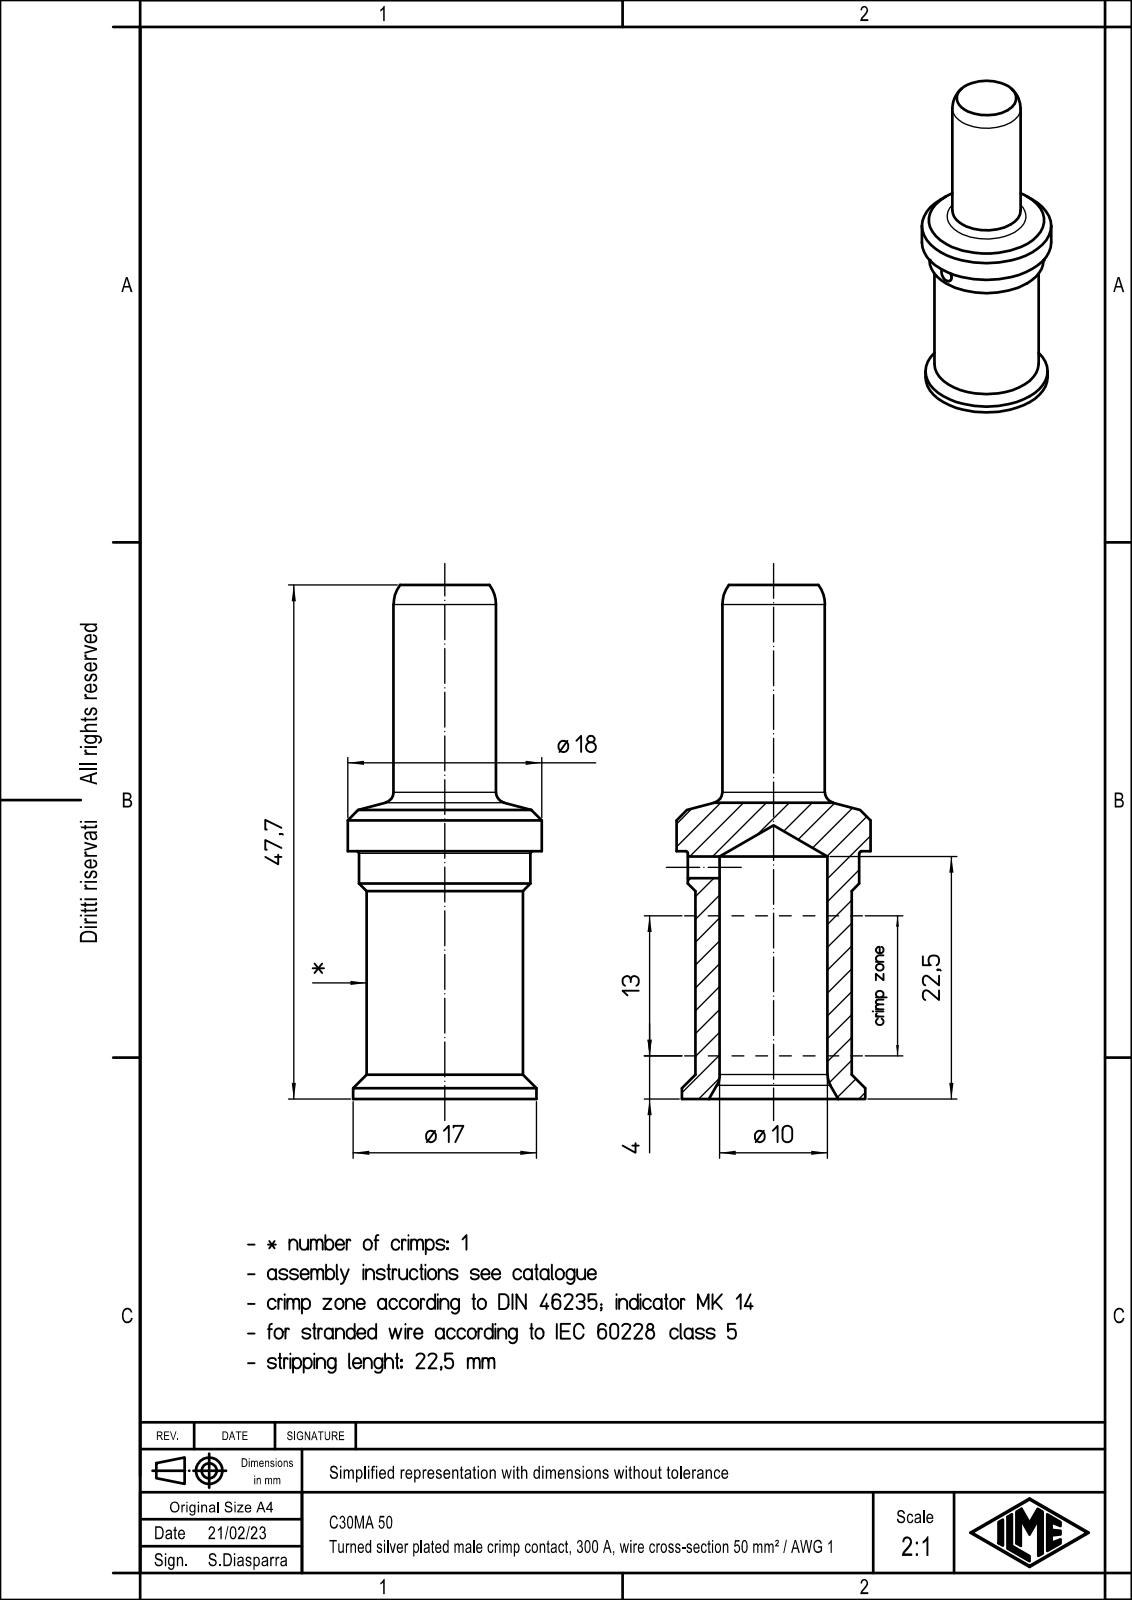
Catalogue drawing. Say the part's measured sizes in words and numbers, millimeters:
The part is named "C30MA 50". Its 3-D file was written by "Creo Elements/Direct Modeling 20.1B 02-Apr-2019 (C) Parametric Technology GmbH (AUTOMOTIVE_DESIGN)". It is 1 solid with 37 faces: 3 planar, 14 cylindrical and 20 other. Overall it measures 47.7 by 18 by 18 millimeters. Its volume is 4 601 cubic millimeters and its surface area 3 121 square millimeters. Round holes: 1 of diameter 2, 1 of diameter 10. Round bosses or shafts: 1 of diameter 18, 1 of diameter 17, 1 of diameter 15.9, 1 of diameter 14.5, 1 of diameter 9.5. The main face-to-face distances are 47.7, 23, 24.7.
